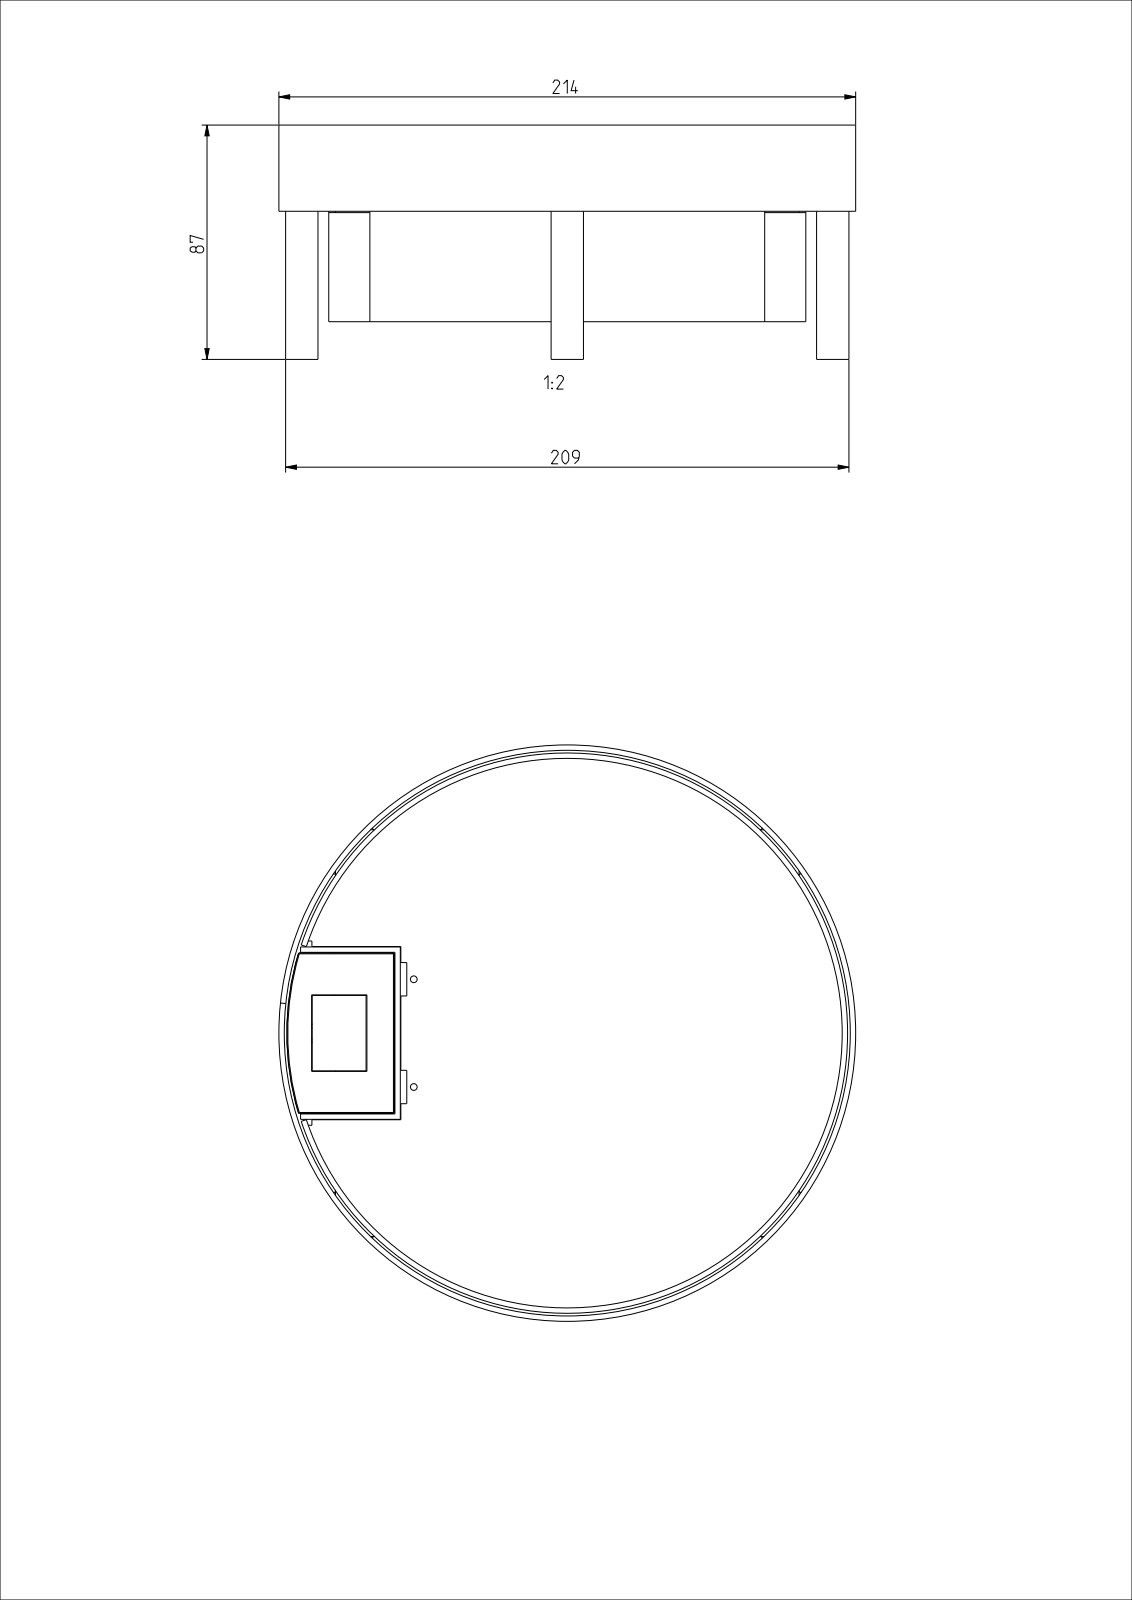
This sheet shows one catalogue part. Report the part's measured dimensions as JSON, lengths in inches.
{"part_name": "T-00671; T-00672; T-00673; T-00675 (+8 more)", "step_written_by": "CREO PARAMETRIC BY PTC INC, 2022024 (AUTOMOTIVE_DESIGN)", "units": "inches", "bodies": {"solids": 15, "faces": 290, "planar": 187, "cylindrical": 85, "other": 18}, "overall_size": [8.425, 8.425, 3.425], "volume_in3": 14.85, "surface_area_in2": 381.8, "round_holes": [[0.15, 6], [0.268, 4], [0.335, 4], [0.398, 4], [0.098, 2], [8.268, 1]], "round_bosses_or_shafts": [[0.472, 4], [0.388, 4], [8.425, 1], [8.189, 1], [8.031, 1]], "partial_cylinders_radius": [[0.02, 10], [0.012, 3], [0.04, 1], [0.26, 1]], "face_to_face_distances": [0.079, 0.098, 0.197, 6.043, 0.276, 0.118, 6.87, 1.063, 5.945, 6.142], "hole_center_spacings": [1.62, 3.834, 3.878, 4.187, 5.484, 6.477, 7.54, 0.867]}
